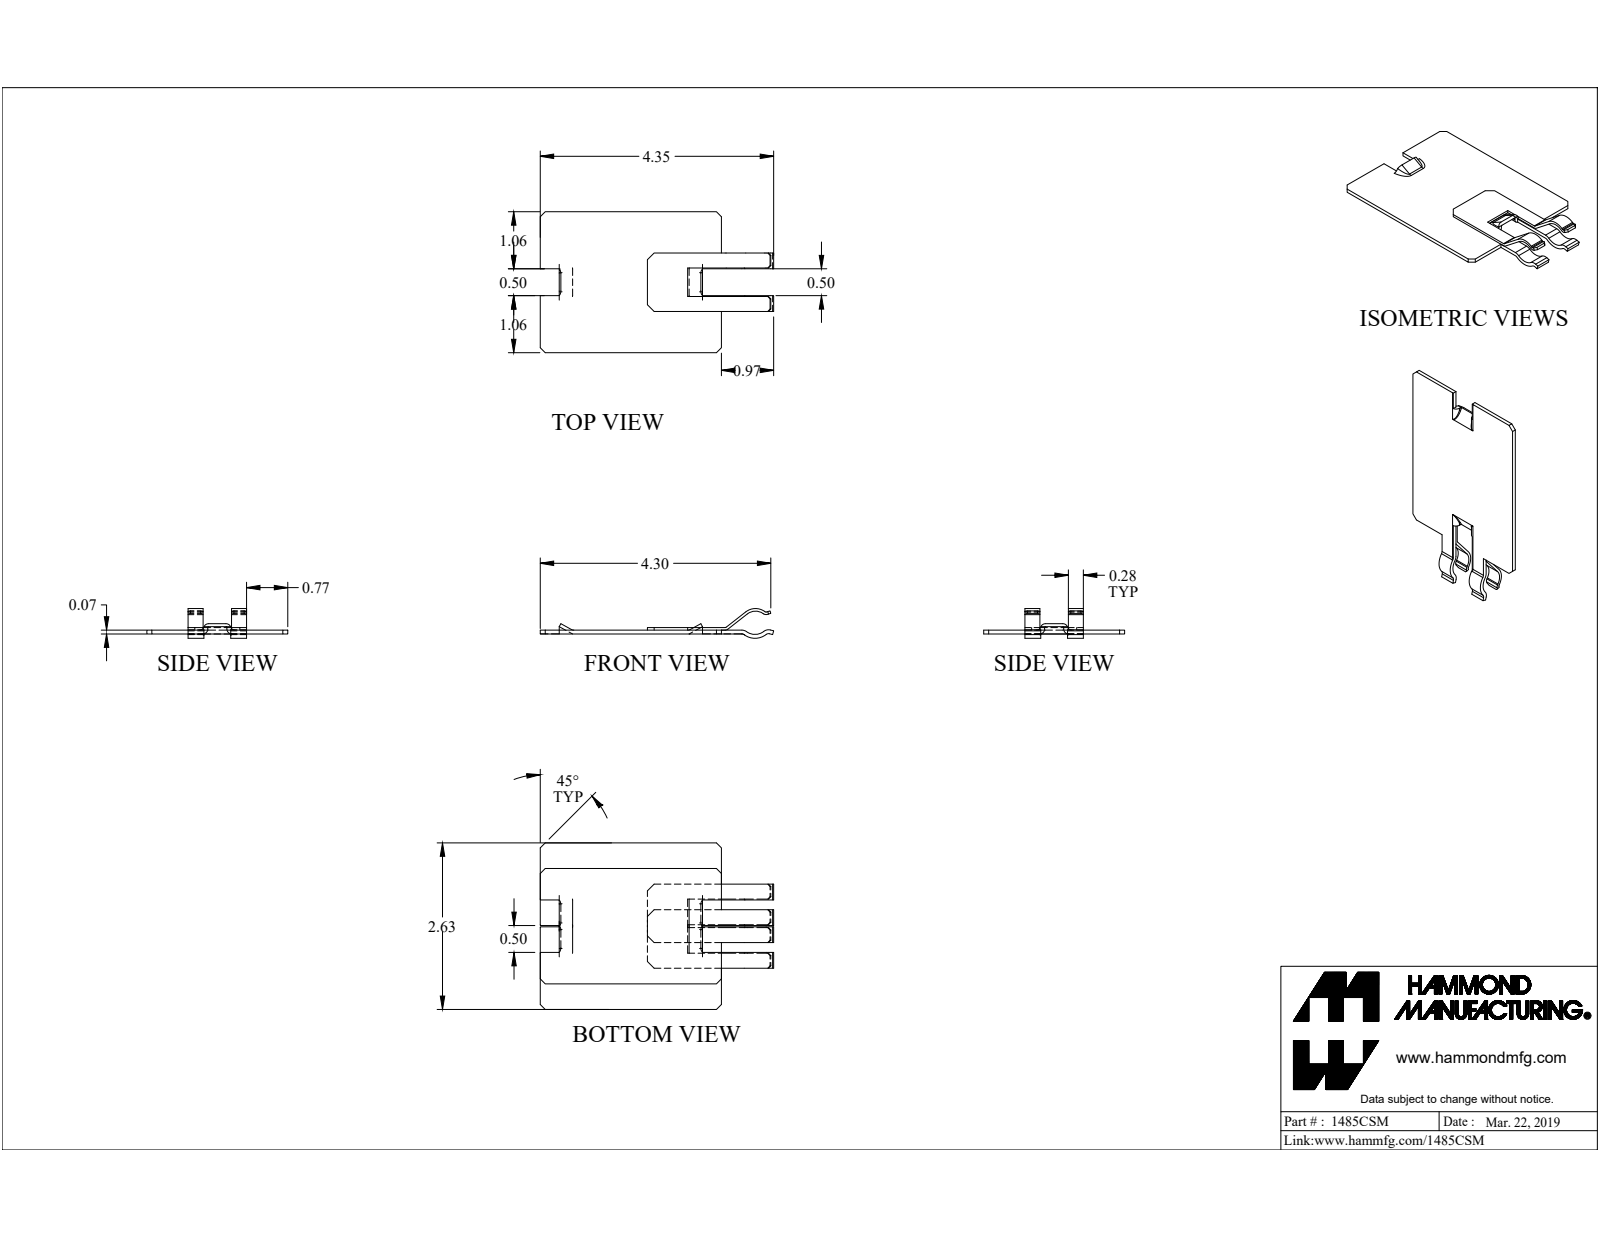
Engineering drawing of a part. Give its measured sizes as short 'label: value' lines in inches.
name: 1485CSM
written by: SolidWorks 2019 (CONFIG_CONTROL_DESIGN)
unit: in
bodies: 4 solids, 127 faces (79 planar, 38 cylindrical, 10 other)
size: 4.348 × 2.625 × 0.599
volume: 1.23 in³; area: 33.01 in²
rounds: 8× R0.09, 4× R0.015, 3× R0.072, 2× R0.144, 1× R0.024, 1× R0.03, 1× R0.078, 1× R0.245
face distances: 0.072, 0.125, 0.197, 0.048, 0.245, 0.12, 0.75, 2.543, 2.625, 0.768
